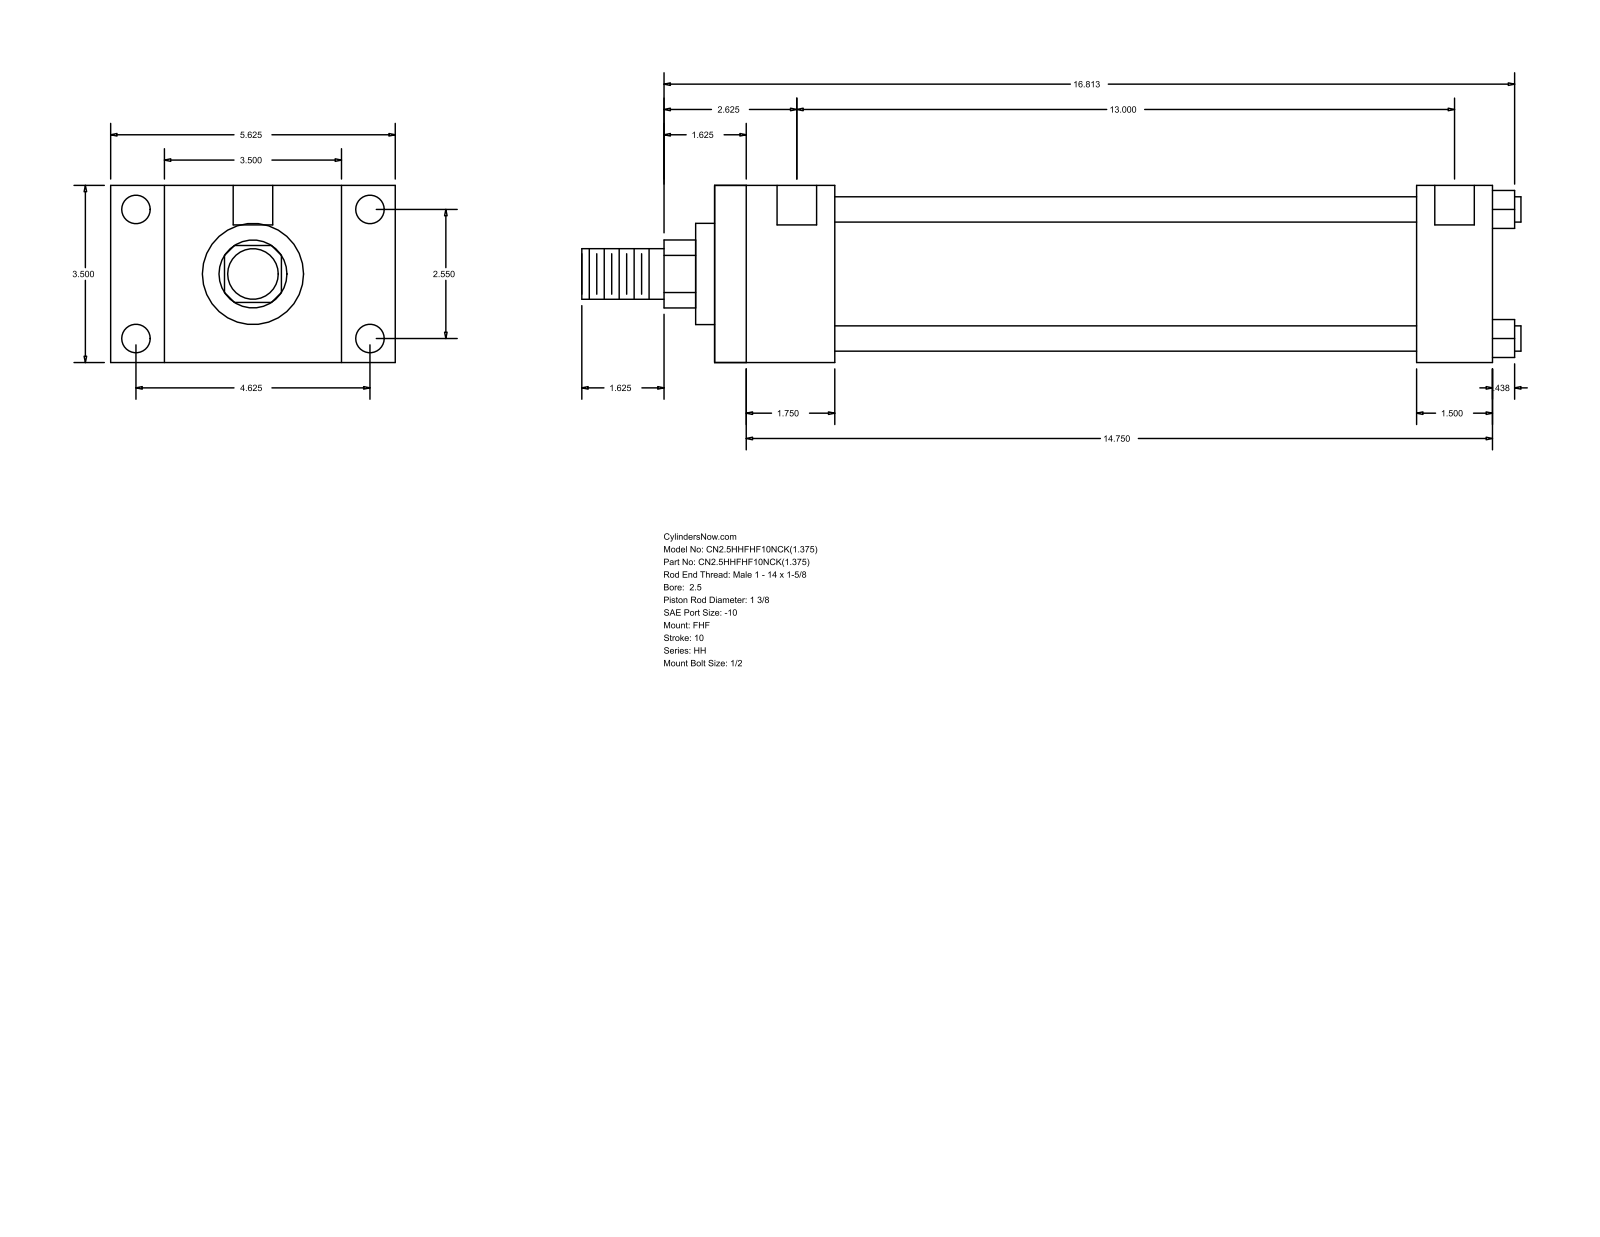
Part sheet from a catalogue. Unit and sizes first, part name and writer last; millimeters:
Units: millimetres
Overall size (bounding box): 471.49 × 142.88 × 88.9
Round holes (diameter × count): ⌀5.56 ×4, ⌀14.3 ×4, ⌀19.84 ×2
Round bosses / shafts (diameter × count): ⌀12.7 ×4, ⌀73.03 ×1, ⌀50.8 ×1, ⌀34.92 ×1, ⌀25.4 ×1
Partial cylindrical surfaces — rounded edges, fillets, slot ends (radius × count): R17.06 ×1
Main face-to-face distances: 88.9, 60.32, 26.99, 115.89, 390.53, 330.21, 142.88, 352.42, 292.1, 38.11
Hole centre spacings: 1.58, 64.76, 117.48, 134.15, 331.79, 333.37, 330.21
Bodies: 0 solids, 88 faces (60 planar, 28 cylindrical, 0 other)
Part name (STEP PRODUCT): HH_FHF__0250_1.375
STEP written by: GSSL Pune (CONFIG_CONTROL_DESIGN)
